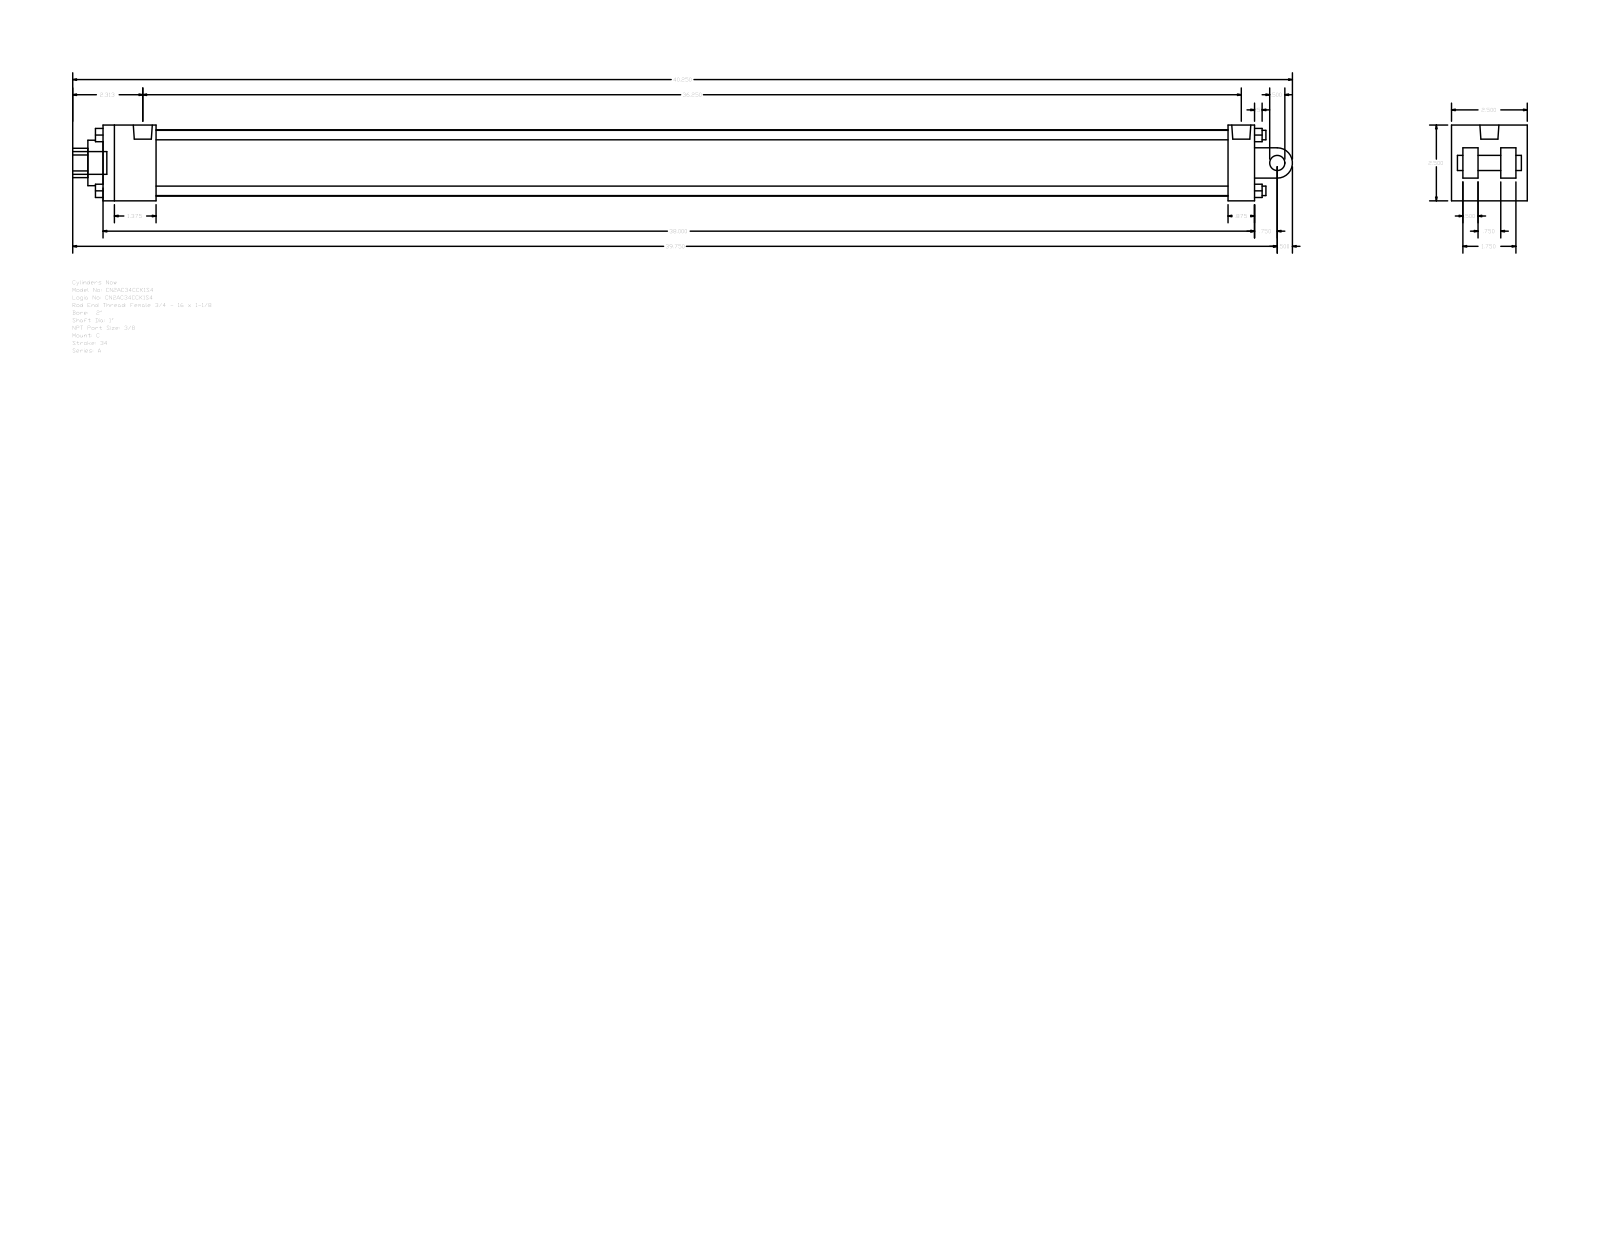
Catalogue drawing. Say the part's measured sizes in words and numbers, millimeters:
The part is named "A_C__0200_1". Its 3-D file was written by "GSSL Pune (CONFIG_CONTROL_DESIGN)". It is 0 solids with 135 faces: 102 planar, 33 cylindrical and 0 other. Overall it measures 1022.35 by 63.5 by 63.5 millimeters. Round holes: 2 of diameter 5.56, 1 of diameter 15.93, 1 of diameter 25.4, 1 of diameter 38.1, 1 of diameter 55.63. Round bosses or shafts: 4 of diameter 7.94, 2 of diameter 5.56, 1 of diameter 19.05, 1 of diameter 15.93, 1 of diameter 12.7. Partial cylindrical surfaces (rounded edges, fillets, slot ends): 1 of radius 12.29, 1 of radius 12.7. The main face-to-face distances are 63.5, 22.22, 965.2, 44.45, 12.7, 9.52, 41.28, 920.75, 942.98, 898.53. The hole center spacings are 3.98.
